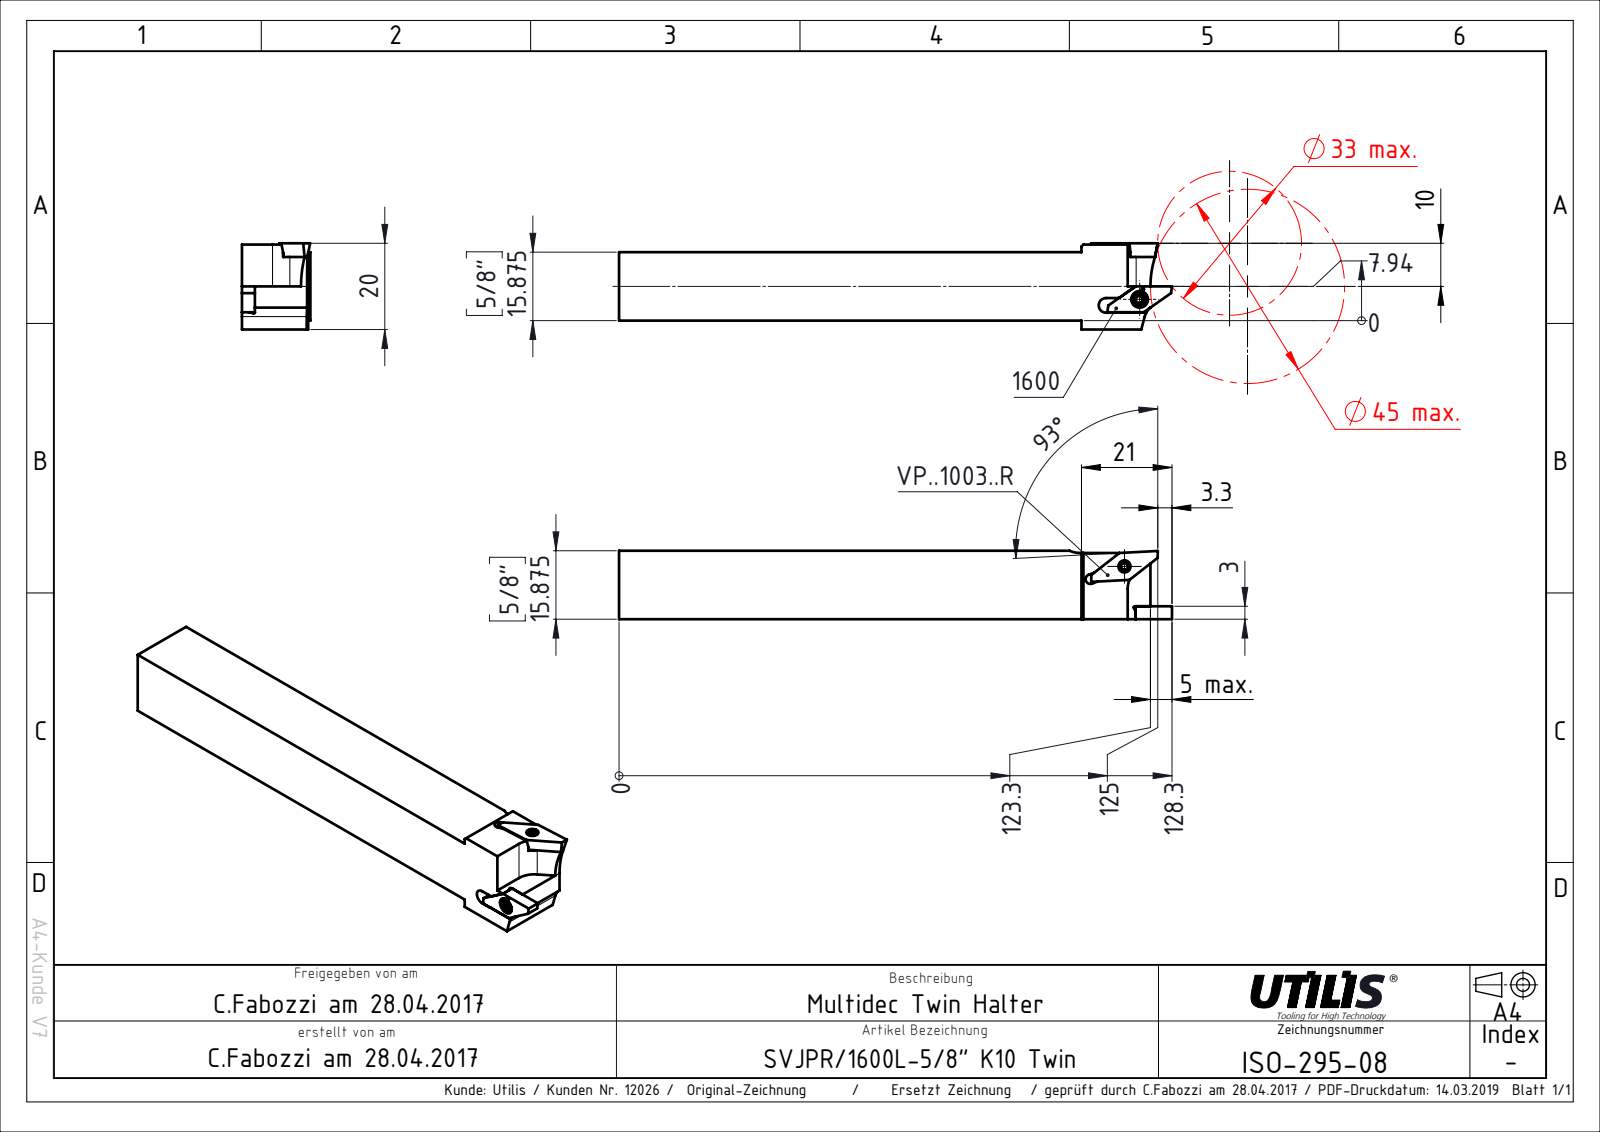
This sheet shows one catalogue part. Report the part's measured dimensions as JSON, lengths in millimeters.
{"part_name": "ISO-295-08", "step_written_by": "SolidWorks 2016 (AUTOMOTIVE_DESIGN)", "units": "millimeters", "bodies": {"solids": 1, "faces": 75, "planar": 61, "cylindrical": 12, "other": 2}, "overall_size": [128.3, 20, 15.88], "volume_mm3": 31180, "surface_area_mm2": 8718, "partial_cylinders_radius": [[0.25, 2], [6.1, 2], [0.5, 1], [1.1, 1], [1.55, 1], [1.7, 1], [4.1, 1], [5.1, 1]], "face_to_face_distances": [15.88, 2.06, 17.94, 15.41, 0.47, 7.94, 10, 19.7, 17.64, 1.76]}
